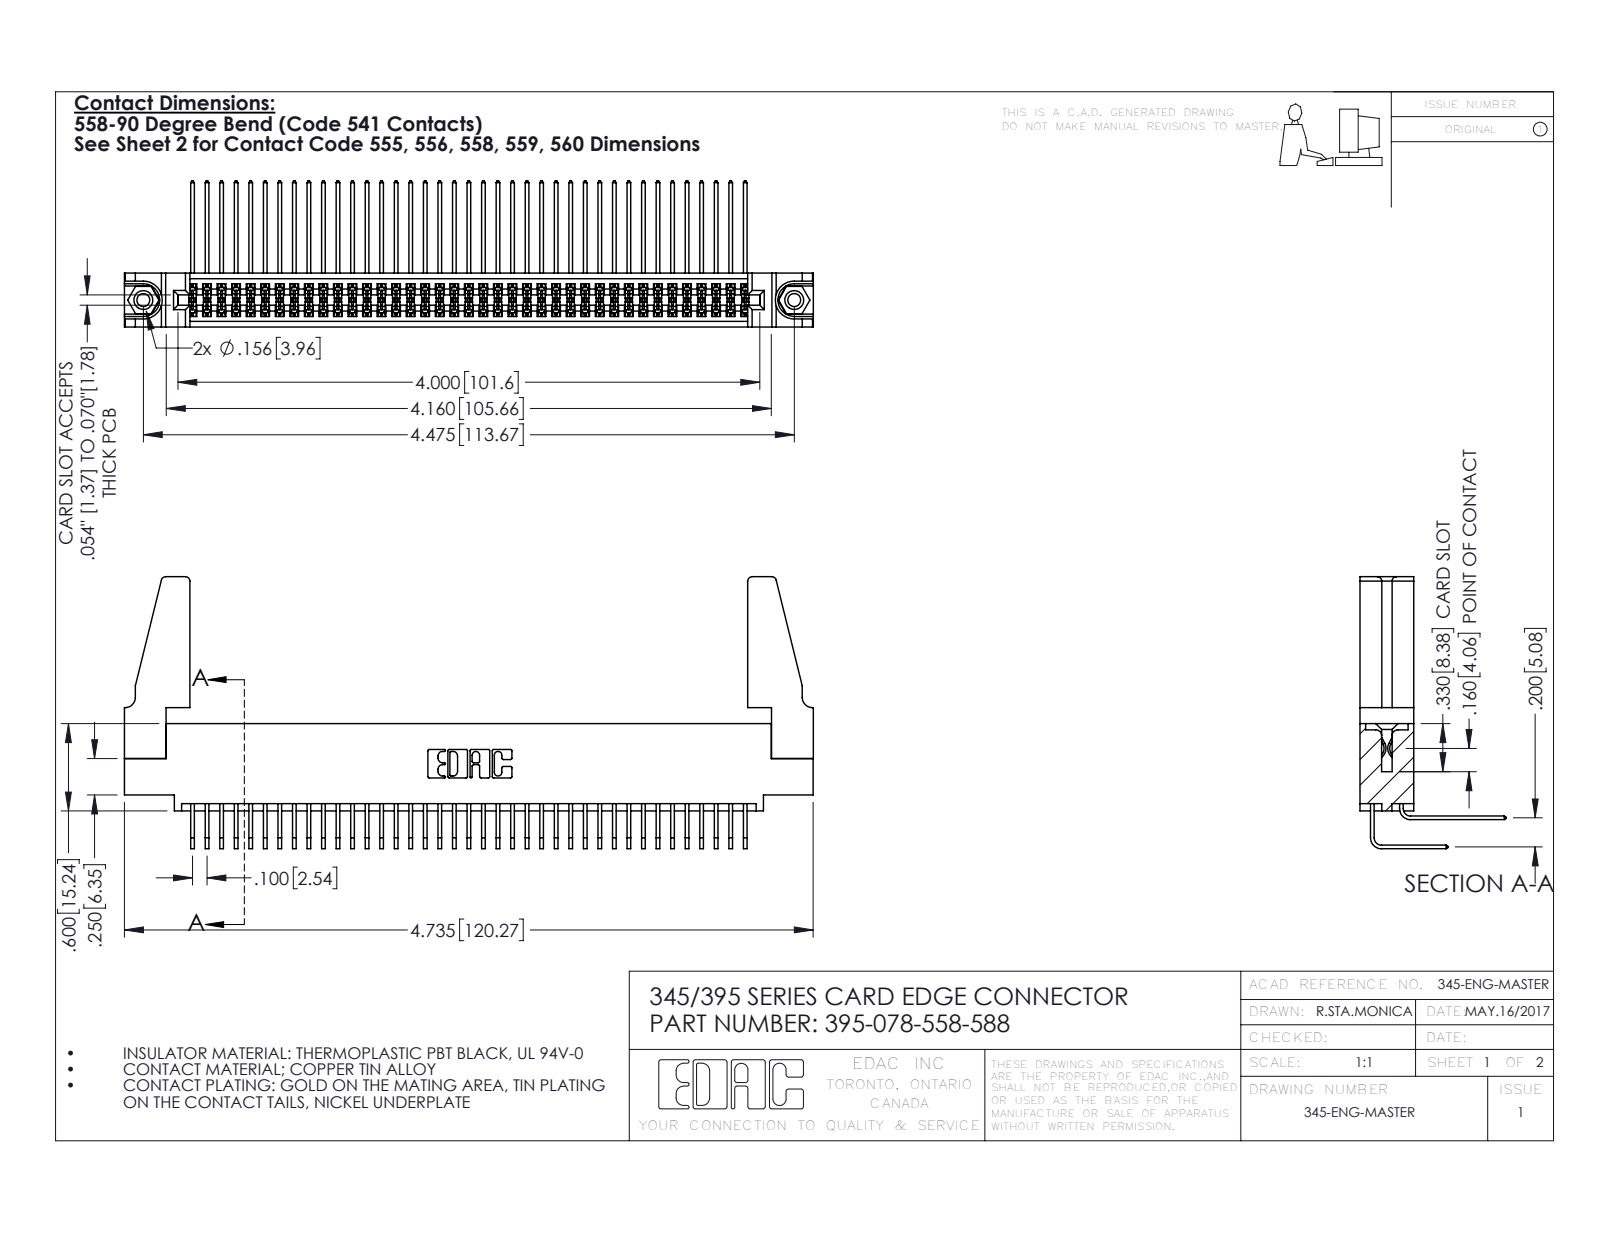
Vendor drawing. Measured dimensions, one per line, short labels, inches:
name: 345-250-001_345-250-001-102; 345-292-001_558 559 Tail - 1; 345-292-001_558 Tail - 2; 345-220-078_345-220-088 (+2 more)
written by: SolidWorks 2016 (CONFIG_CONTROL_DESIGN)
unit: in
bodies: 83 solids, 4310 faces (2886 planar, 1408 cylindrical, 16 other)
size: 4.736 × 1.869 × 1.005
volume: 0.933 in³; area: 35.75 in²
holes: 2× ⌀0.089, 2× ⌀0.125, 2× ⌀0.156, 1× ⌀0.064
bosses: 2× ⌀0.155
rounds: 118× R0.006, 22× R0.01, 8× R0.03, 6× R0.007, 6× R0.031, 3× R0.026, 2× R0.014, 2× R0.019
face distances: 0.072, 0.298, 0.2, 0.37, 0.098, 0.272, 0.025, 0.225, 0.025, 0.175
hole spacings: 0.27, 4.239, 4.475
